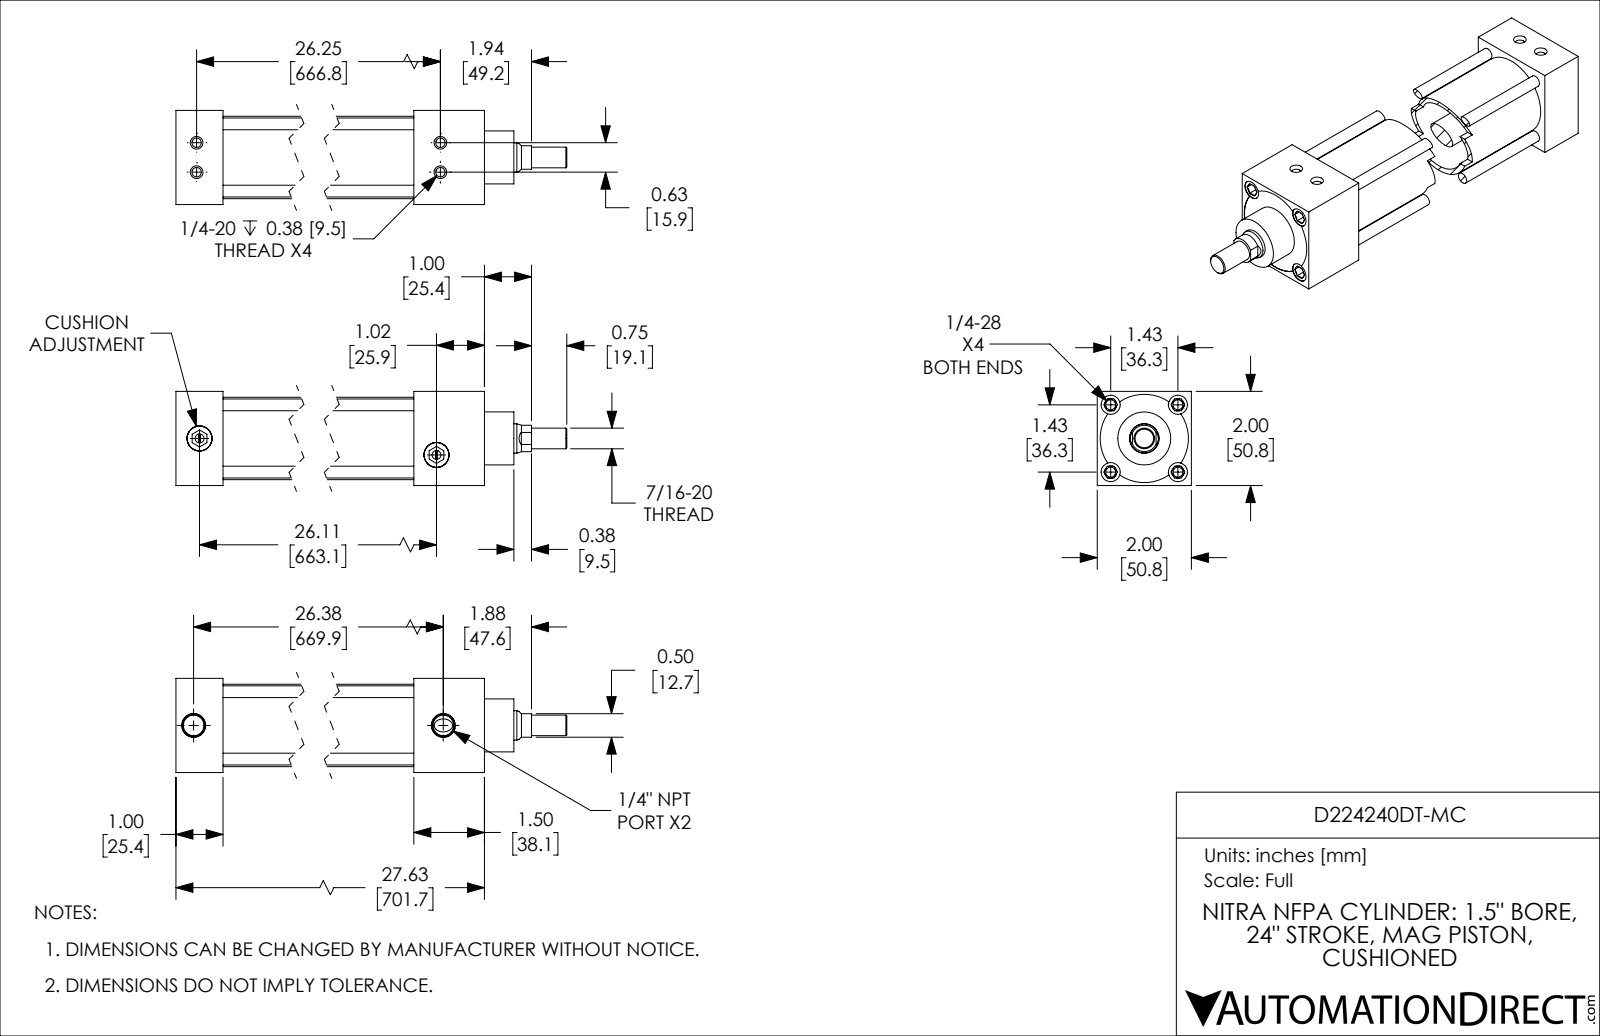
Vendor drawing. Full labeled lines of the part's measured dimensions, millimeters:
Part name (STEP PRODUCT): D224240DT-MC_CUSHION; D224240DT-MC_PISTON_KK1; D224240DT-MC; D224240DT-MC_BODY
STEP written by: SolidWorks 2019 (CONFIG_CONTROL_DESIGN)
Units: millimetres
Bodies: 4 solids, 251 faces (90 planar, 81 cylindrical, 80 other)
Overall size (bounding box): 746.1 × 50.8 × 50.8
Volume: 664 500 mm³ · Surface area: 288 100 mm²
Round holes (diameter × count): ⌀5.1 ×4, ⌀5.4 ×4, ⌀10.3 ×4, ⌀4.8 ×2, ⌀11.1 ×2, ⌀13.5 ×2, ⌀15.9 ×1, ⌀38.1 ×1
Round bosses / shafts (diameter × count): ⌀6.4 ×4, ⌀13.5 ×2, ⌀44.5 ×1, ⌀38.1 ×1, ⌀28.6 ×1, ⌀15.8 ×1, ⌀11.1 ×1
Partial cylindrical surfaces — rounded edges, fillets, slot ends (radius × count): R7.1 ×1, R23.8 ×1
Main face-to-face distances: 50.8, 25.4, 663.6, 638.2, 701.5, 676.1, 38, 28.6, 54, 609.6
Hole centre spacings: 8.1, 25.7, 36.3, 15.9, 51.4, 666.8, 666.9, 668.4
